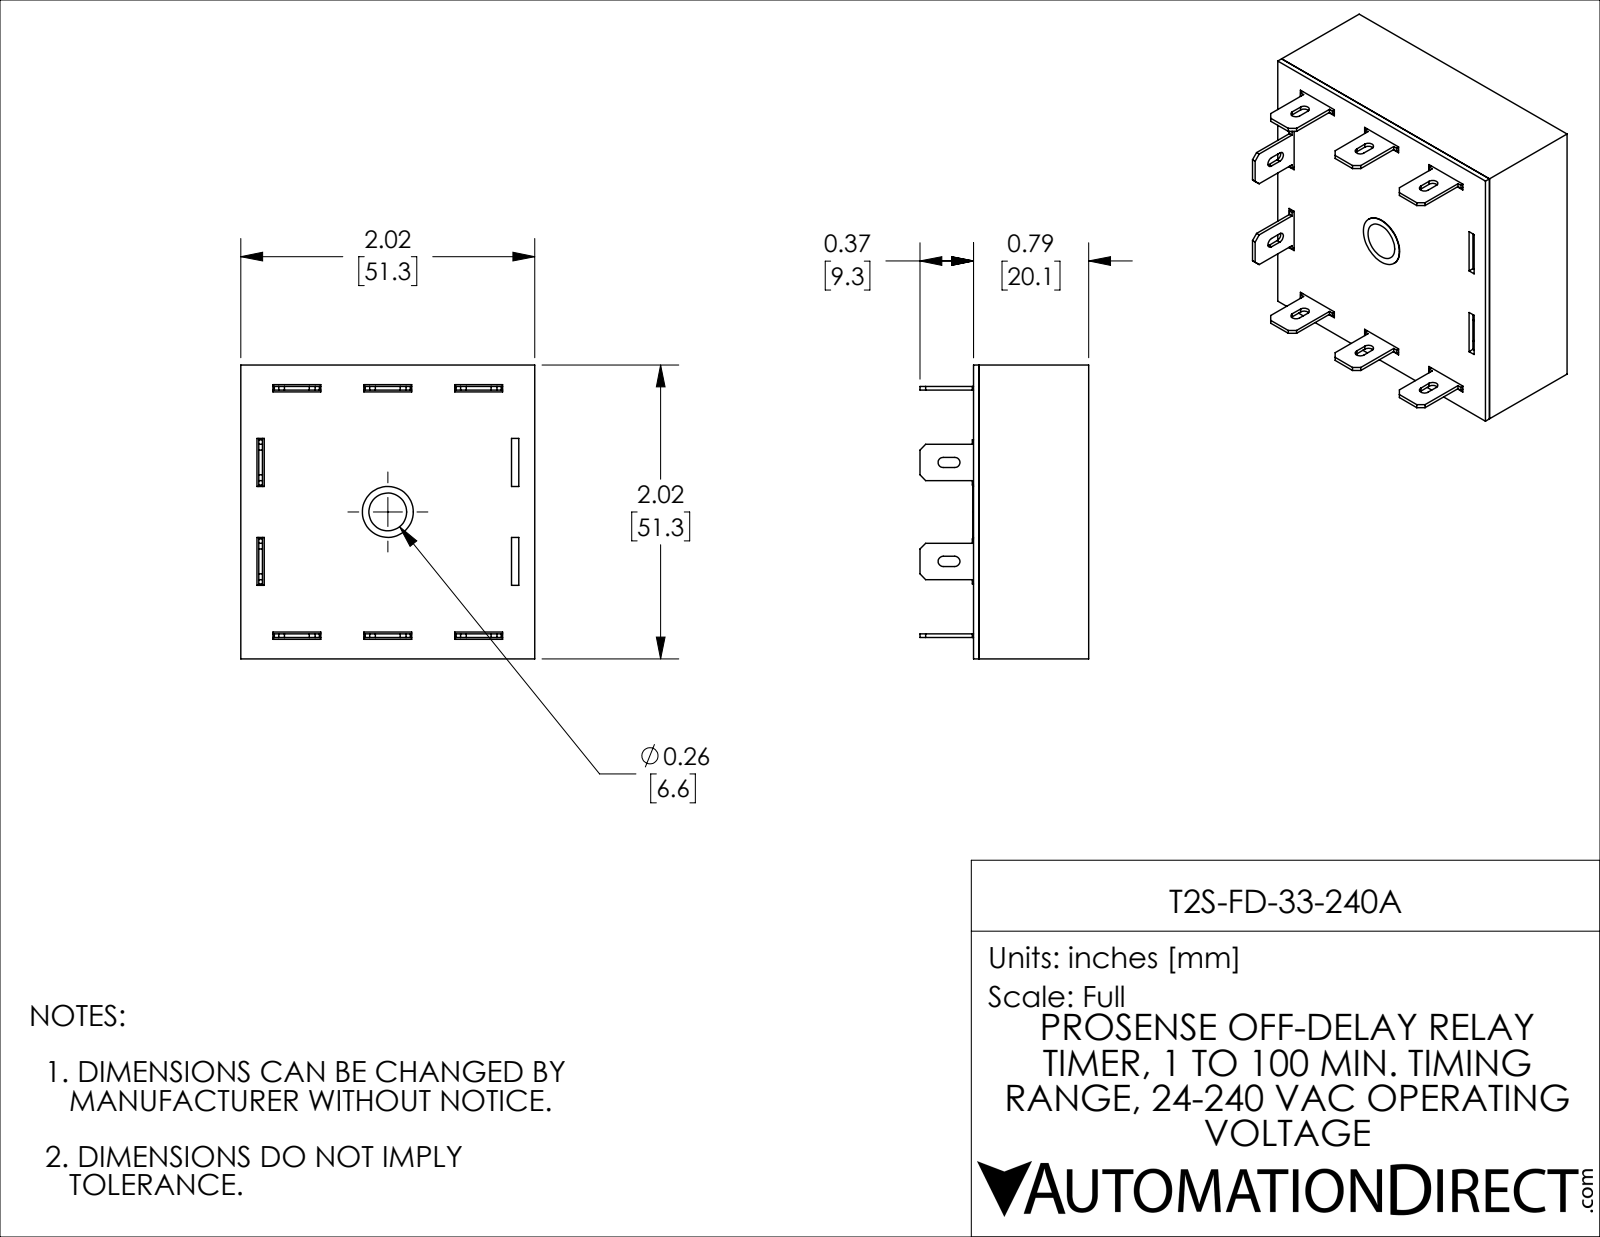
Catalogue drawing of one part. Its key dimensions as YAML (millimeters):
part_name: "T2S-FD-33-240A"
step_written_by: "SolidWorks 2021 (CONFIG_CONTROL_DESIGN)"
units: millimeters
bodies: {solids: 10, faces: 256, planar: 234, cylindrical: 20, other: 2}
overall_size: [51.31, 51.31, 29.46]
volume: 11042
surface_area: 22819
round_holes:
  - {diameter: 8.89, count: 1}
partial_cylinders:
  - {radius: 0.89, count: 10}
face_to_face_distances: [1.14, 50.16, 19.15, 20.12, 0.97, 18.01, 18.98, 51.3, 49.02, 3.74]
